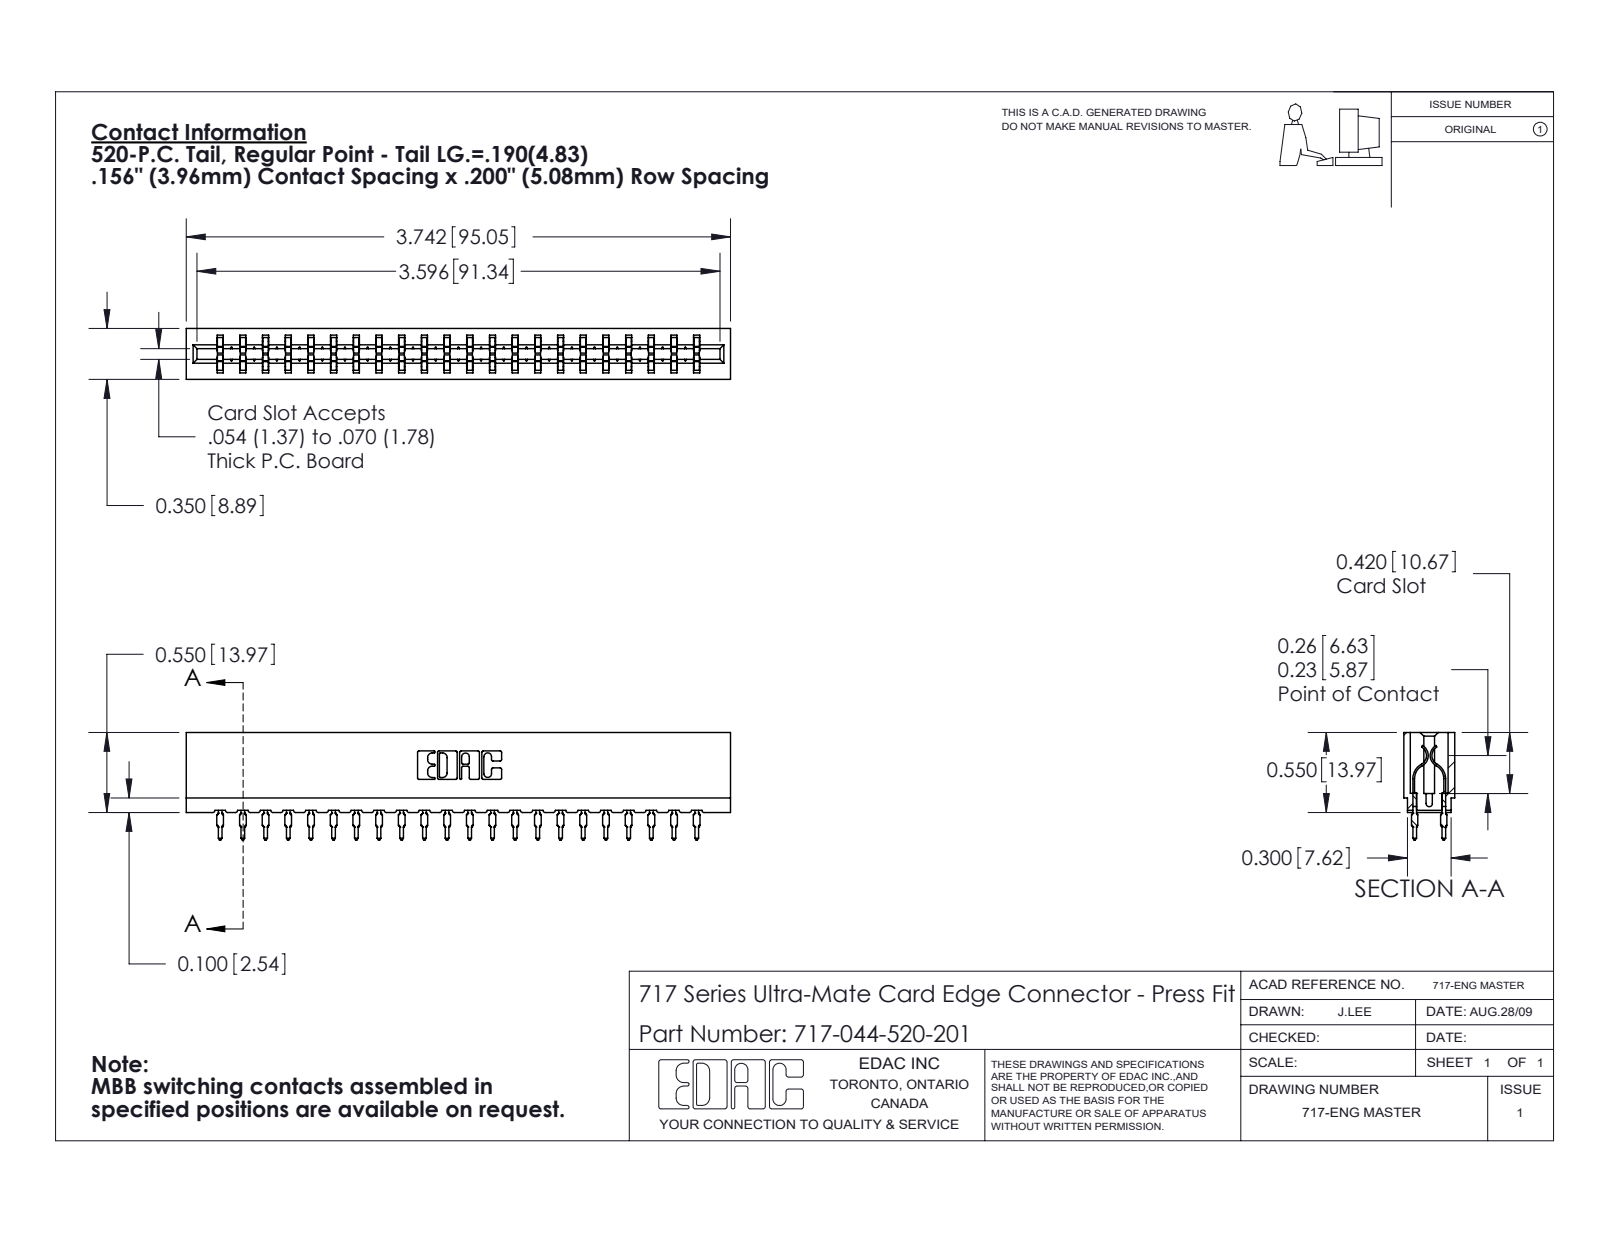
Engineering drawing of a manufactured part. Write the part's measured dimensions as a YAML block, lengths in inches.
part_name: "717 Part_Insulator Option - 06; 745-292-001_520; 717-044-520-201"
step_written_by: "SolidWorks 2020 (CONFIG_CONTROL_DESIGN)"
units: inches
bodies: {solids: 45, faces: 4054, planar: 2100, cylindrical: 810, other: 1144}
overall_size: [3.742, 0.739, 0.35]
volume: 0.505
surface_area: 18.87
partial_cylinders:
  - {radius: 0.021, count: 88}
  - {radius: 0.015, count: 44}
  - {radius: 0.01, count: 22}
  - {radius: 0.005, count: 8}
  - {radius: 0.011, count: 8}
  - {radius: 0.007, count: 6}
  - {radius: 0.031, count: 6}
  - {radius: 0.026, count: 3}
face_to_face_distances: [0.212, 0.138, 0.35, 0.156, 0.063, 0.287, 0.076, 0.149, 0.074, 0.624]
